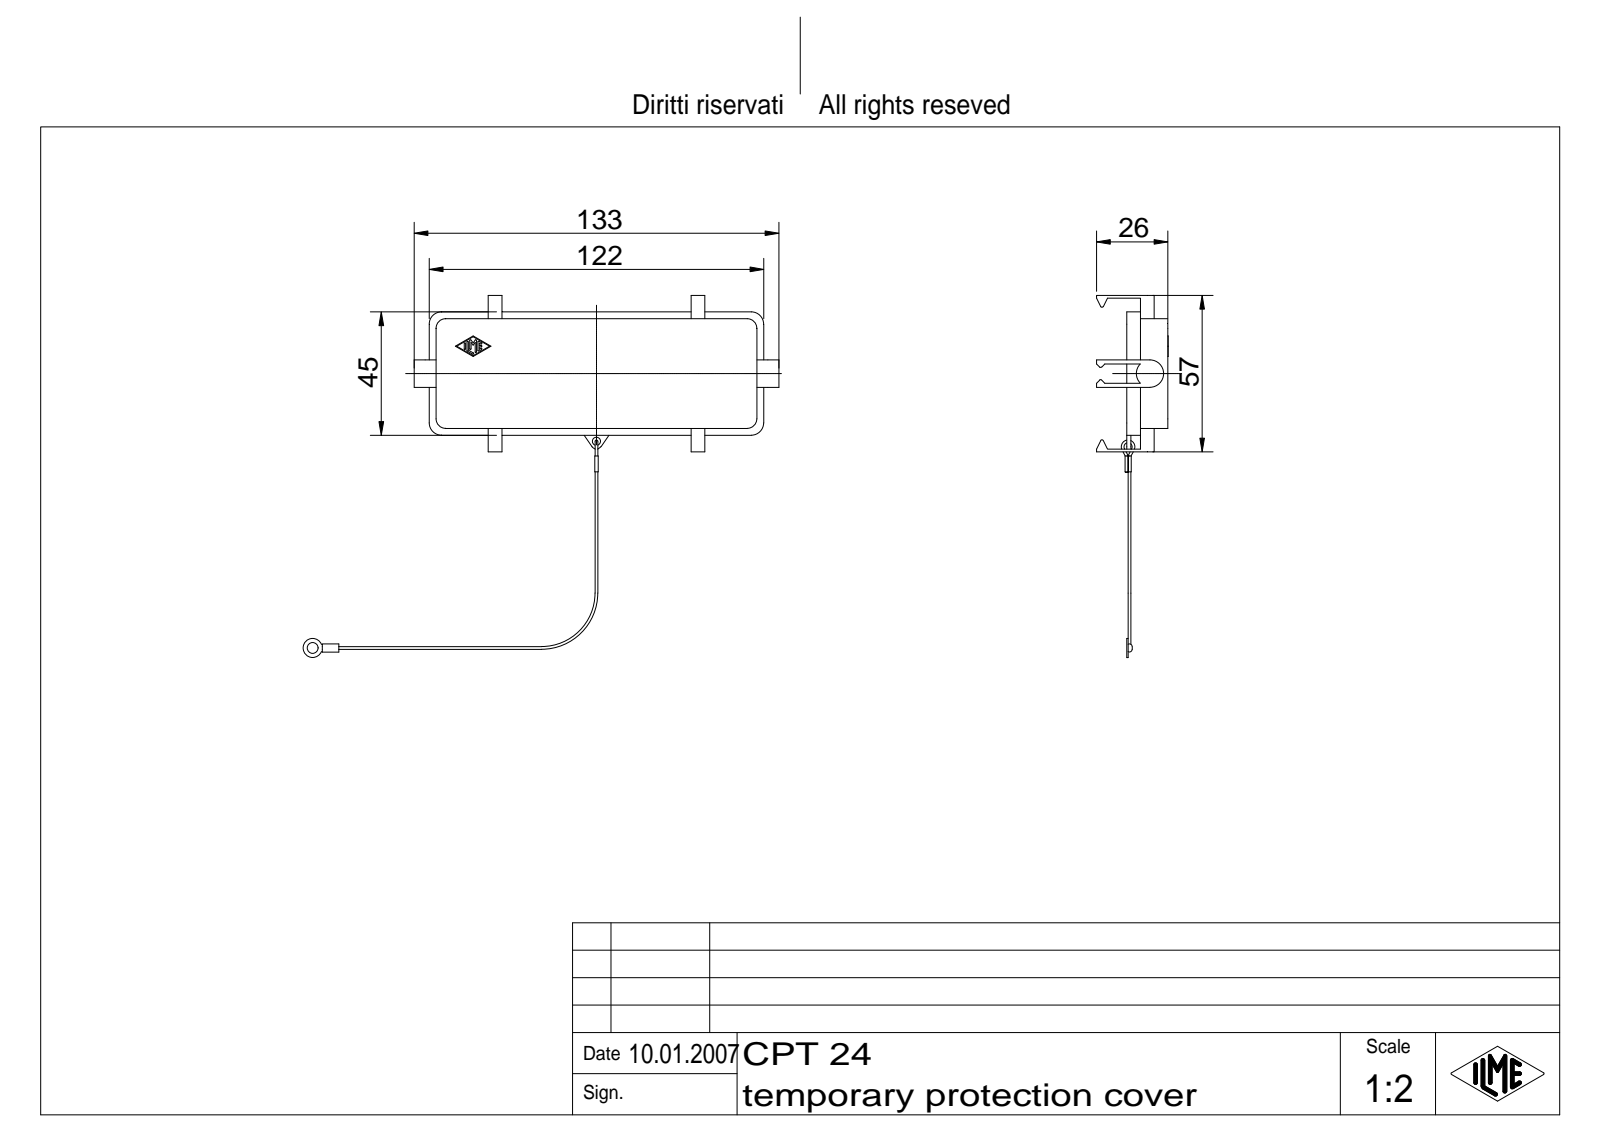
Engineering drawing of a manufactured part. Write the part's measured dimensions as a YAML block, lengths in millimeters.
part_name: "CPT 24"
step_written_by: "Autodesk Inventor 7 (AUTOMOTIVE_DESIGN)"
units: millimeters
bodies: {solids: 2, faces: 235, planar: 116, cylindrical: 74, other: 45}
overall_size: [173.5, 132, 26.1]
volume: 18735
surface_area: 23213
round_holes:
  - {diameter: 3, count: 1}
  - {diameter: 4, count: 1}
round_bosses_or_shafts:
  - {diameter: 1, count: 5}
  - {diameter: 10, count: 1}
  - {diameter: 7, count: 1}
partial_cylinders:
  - {radius: 0.25, count: 14}
  - {radius: 3.5, count: 8}
  - {radius: 2, count: 5}
  - {radius: 4.5, count: 4}
  - {radius: 0.5, count: 3}
  - {radius: 0.62, count: 2}
  - {radius: 1, count: 2}
  - {radius: 2.5, count: 2}
face_to_face_distances: [1.5, 2.5, 38.25, 1.75, 36.5, 4.25, 40.75, 42.5, 8.5, 40]
hole_center_spacings: [127.99]
